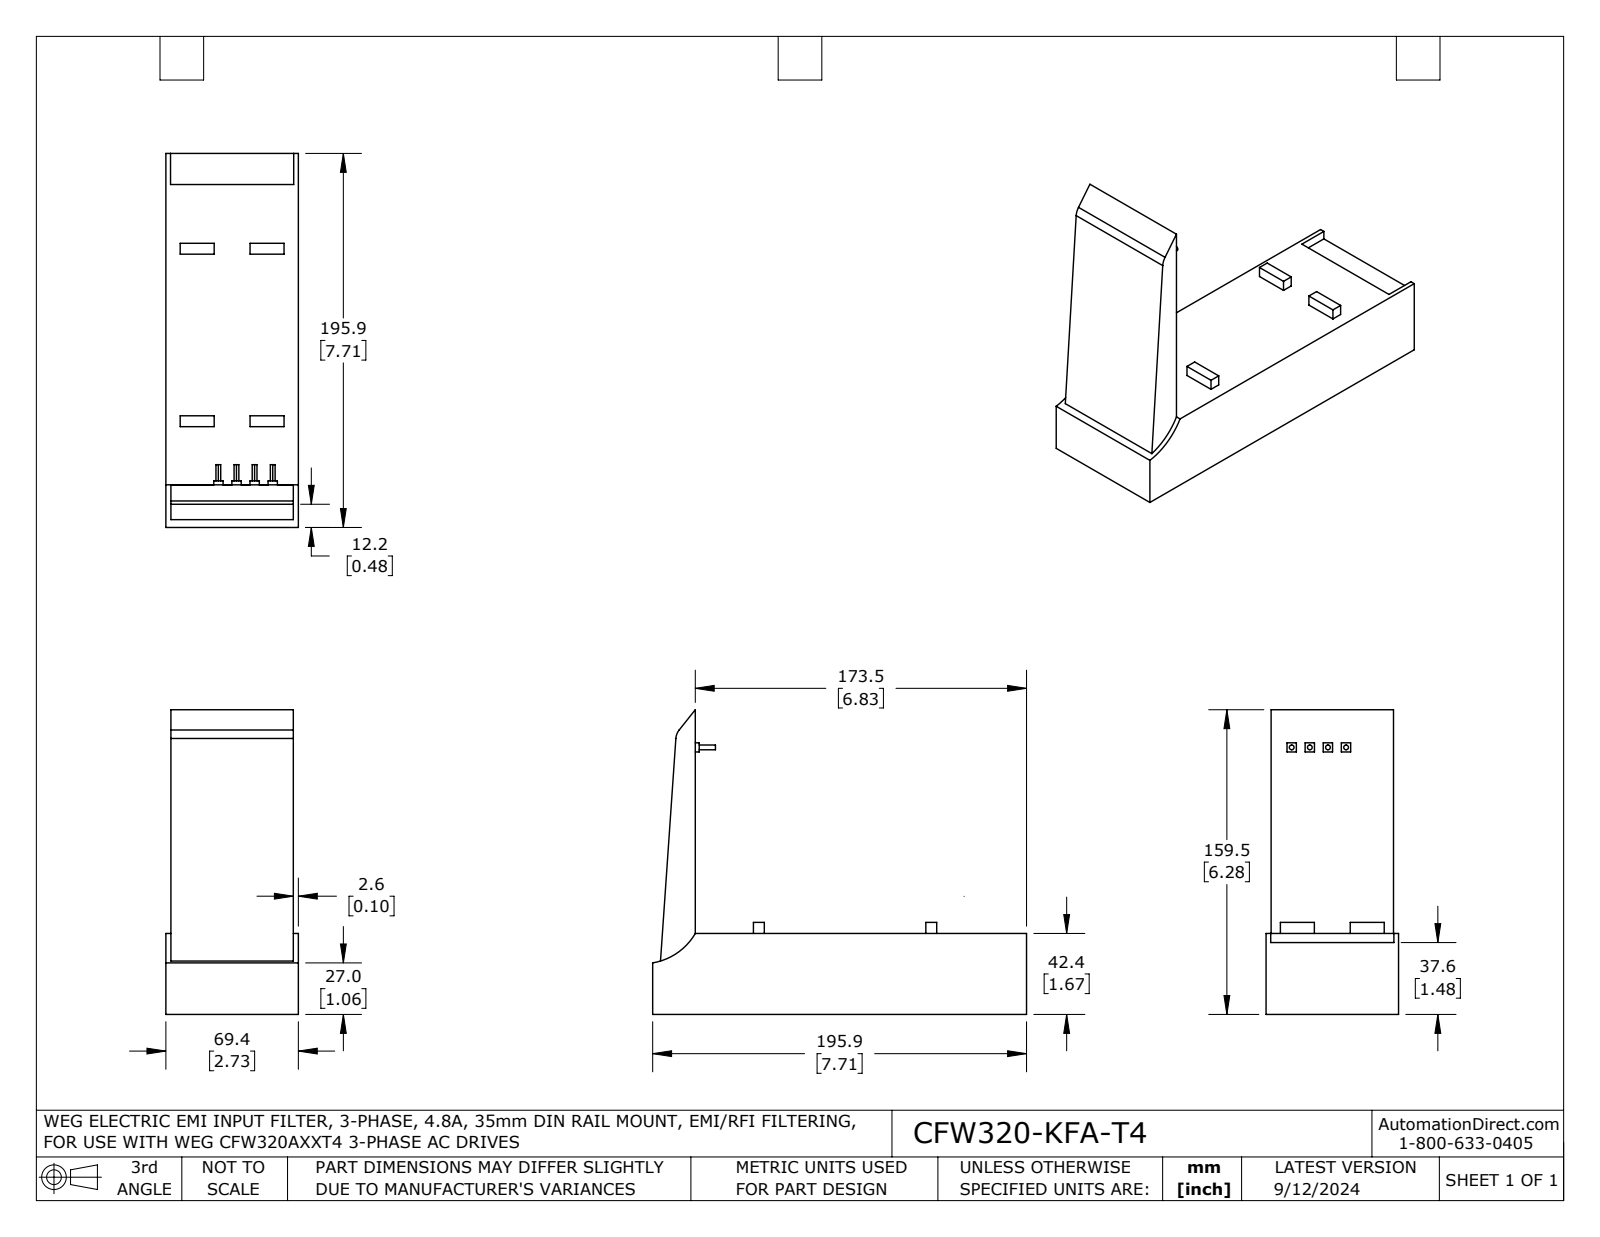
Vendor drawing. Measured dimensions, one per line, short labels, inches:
name: CFW320-KFA-T4
written by: SolidWorks 2021 (AUTOMOTIVE_DESIGN)
unit: in
bodies: 1 solid, 69 faces (59 planar, 10 cylindrical, 0 other)
size: 7.711 × 6.281 × 2.732
volume: 40.51 in³; area: 105.7 in²
bosses: 4× ⌀0.098
rounds: 1× R0.315, 1× R1.26
face distances: 1.669, 2.733, 6.832, 7.711, 0.879, 0.104, 2.628, 2.629, 2.524, 0.104
